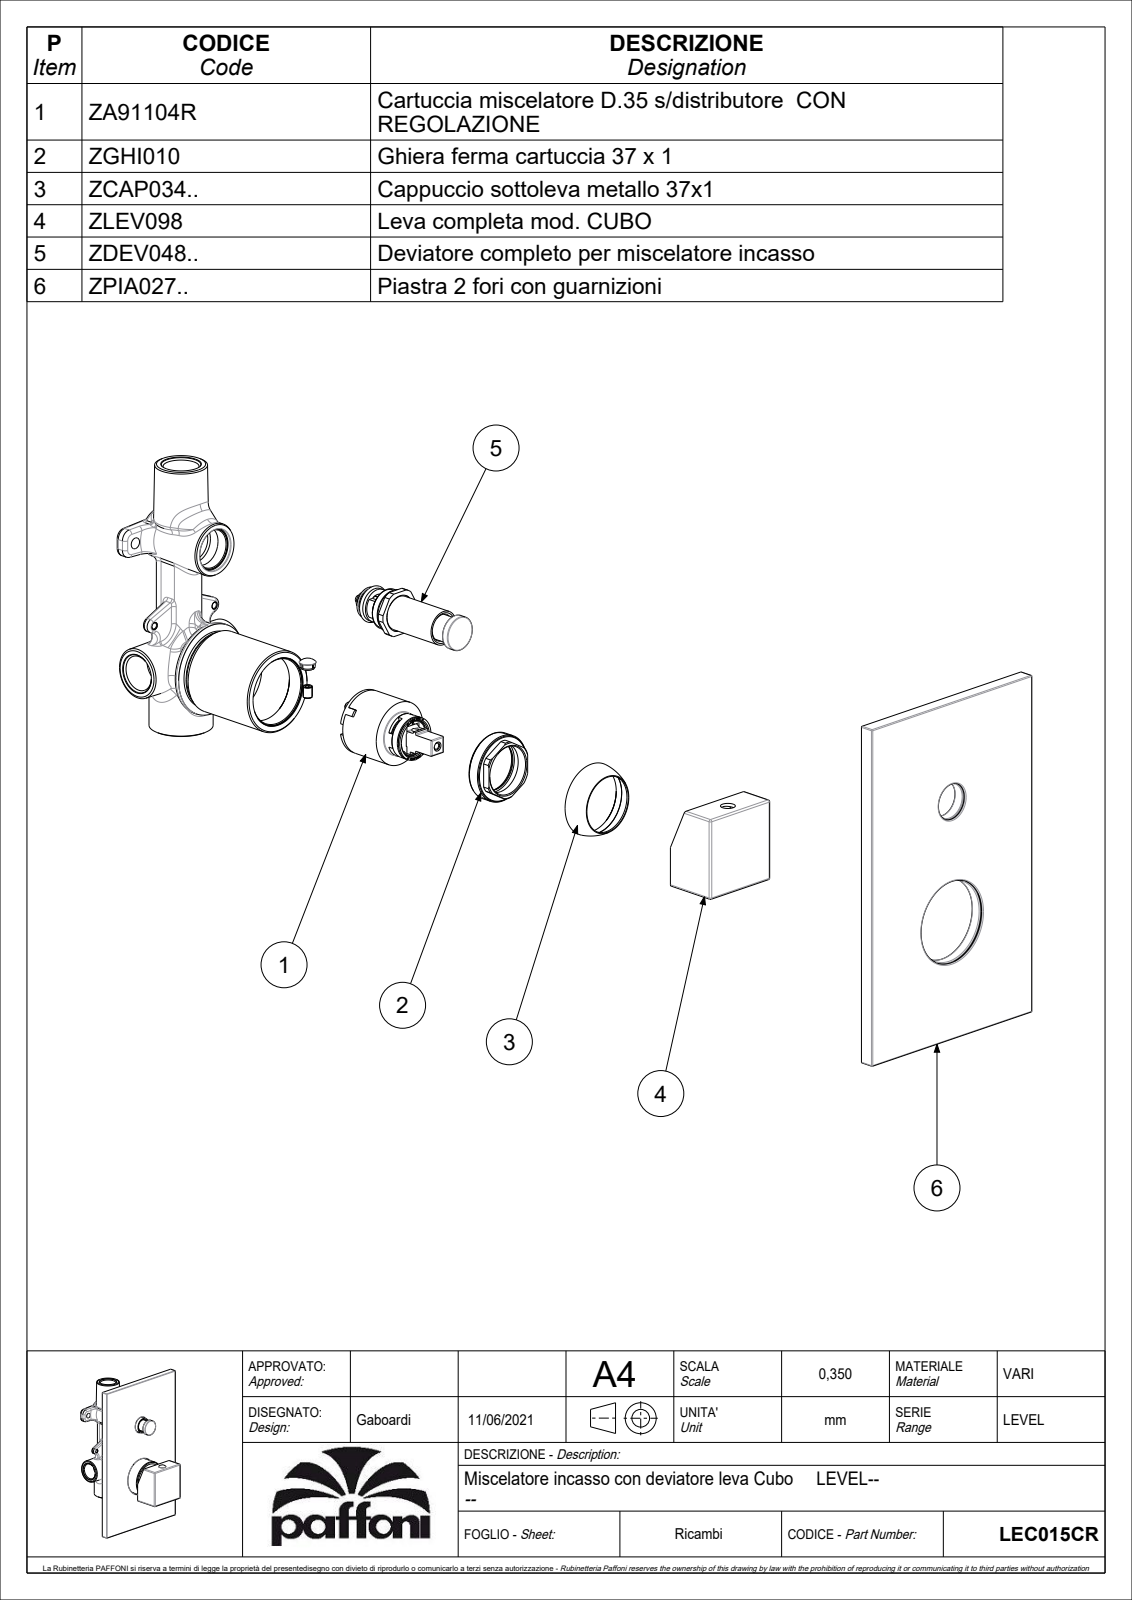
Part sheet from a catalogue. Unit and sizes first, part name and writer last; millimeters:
Units: millimetres
Overall size (bounding box): 190 × 120 × 59.55
Round holes (diameter × count): ⌀4 ×2, ⌀3.3 ×1, ⌀5 ×1, ⌀6 ×1, ⌀10.5 ×1, ⌀11 ×1, ⌀14.8 ×1, ⌀19.2 ×1, ⌀19.5 ×1, ⌀19.9 ×1, ⌀20 ×1, ⌀21 ×1
Round bosses / shafts (diameter × count): ⌀51 ×1, ⌀49 ×1, ⌀44.8 ×1, ⌀35 ×1, ⌀32.2 ×1, ⌀25 ×1, ⌀23.5 ×1, ⌀23.4 ×1
Partial cylindrical surfaces — rounded edges, fillets, slot ends (radius × count): R0.5 ×35, R1 ×18, R0.15 ×11, R0.3 ×4, R3.95 ×1, R7 ×1, R9.3 ×1, R10.85 ×1
Main face-to-face distances: 2.5, 5.5, 8, 0.5, 3, 5, 51.3, 22.5, 37.5, 82.5
Hole centre spacings: 14.1, 68
Volume: 171 951 mm³ · Surface area: 118 000 mm²
Bodies: 5 solids, 1031 faces (603 planar, 257 cylindrical, 171 other)
Part name (STEP PRODUCT): LEC015CR
STEP written by: CREO PARAMETRIC BY PTC INC, 2020044 (CONFIG_CONTROL_DESIGN)
